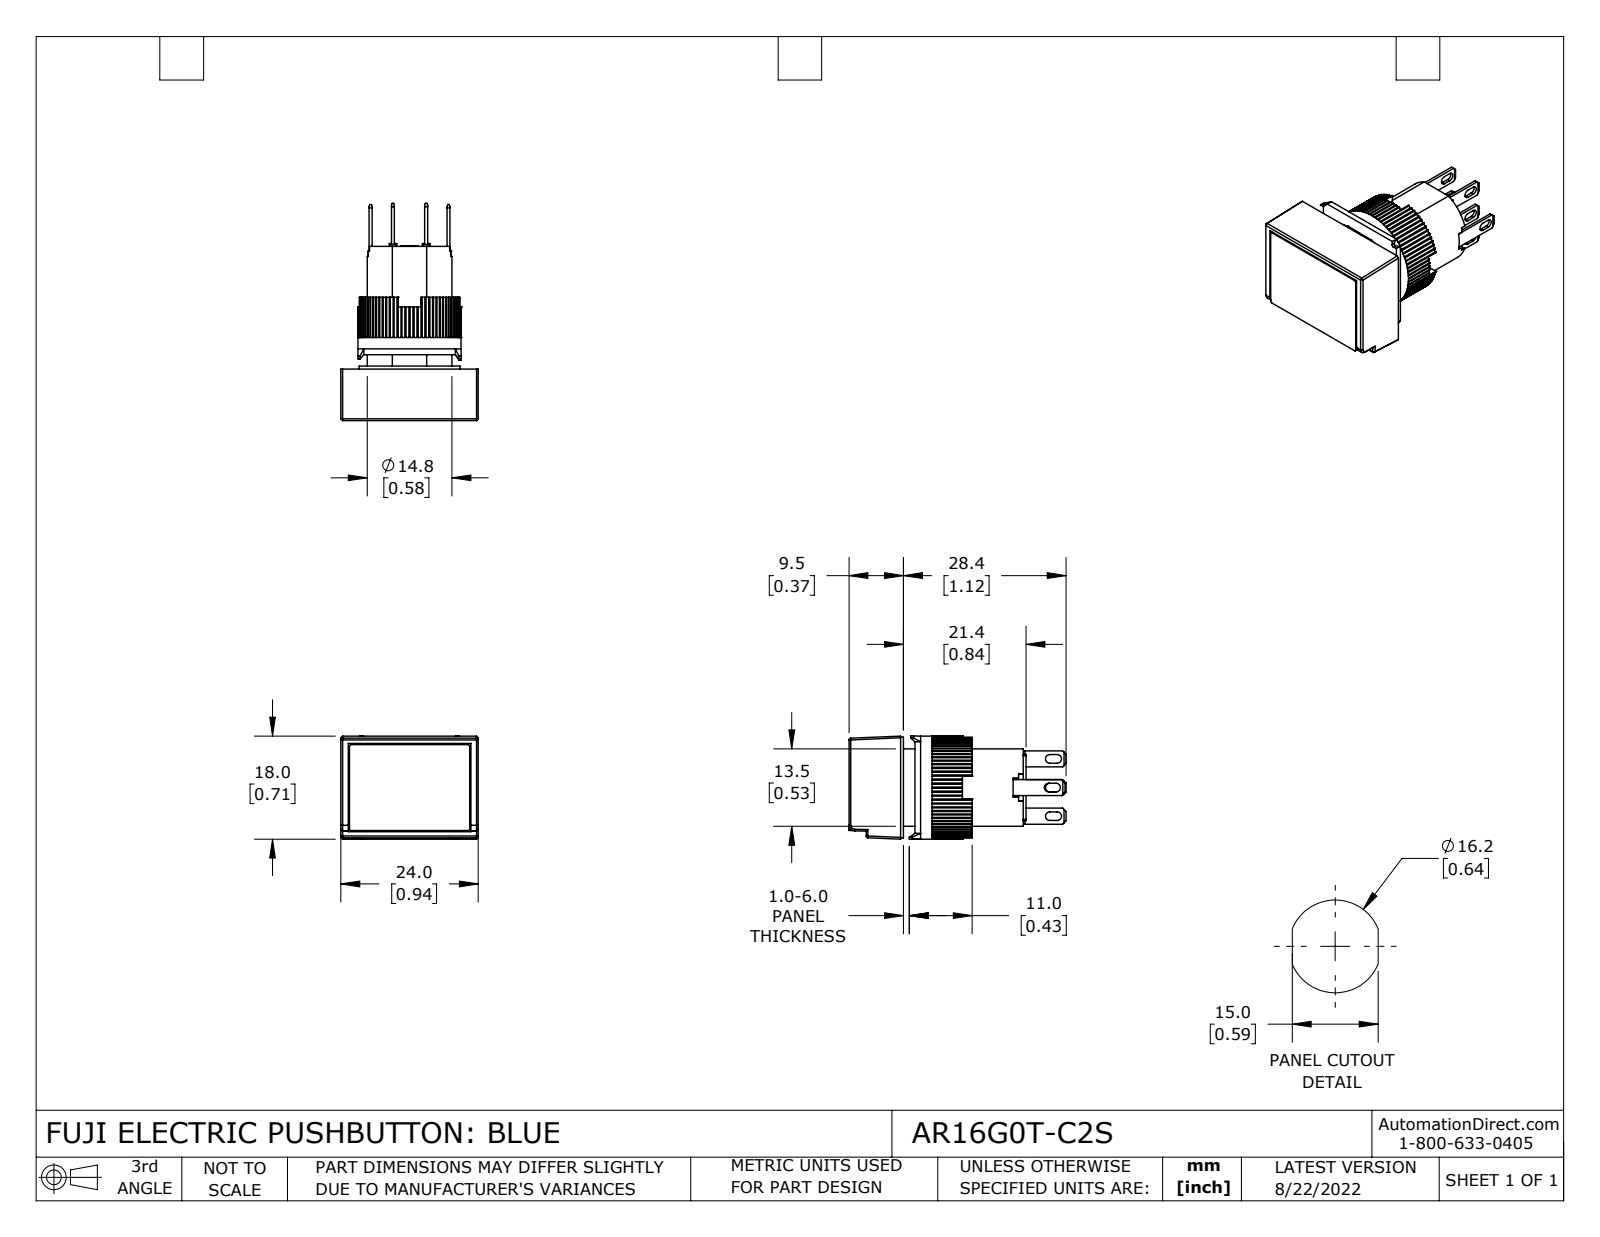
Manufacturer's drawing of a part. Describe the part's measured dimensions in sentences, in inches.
The part is named "AR16G0T-C2S". Its 3-D file was written by "SolidWorks 2021 (CONFIG_CONTROL_DESIGN)". It is 14 solids with 841 faces: 654 planar, 181 cylindrical and 6 other. Overall it measures 1.492 by 0.945 by 0.709 inches. Its volume is 0.448 cubic inches and its surface area 9.503 square inches. Round holes: 1 of diameter 0.543, 1 of diameter 0.583. Round bosses or shafts: 1 of diameter 0.709, 1 of diameter 0.693. Partial cylindrical surfaces (rounded edges, fillets, slot ends): 80 of radius 0.01, 12 of radius 0.008, 8 of radius 0.03, 6 of radius 0.012, 1 of radius 0.039. The main face-to-face distances are 0.213, 0.354, 0.142, 0.35, 0.492, 0.138, 0.02, 0.843, 0.059, 0.453.
